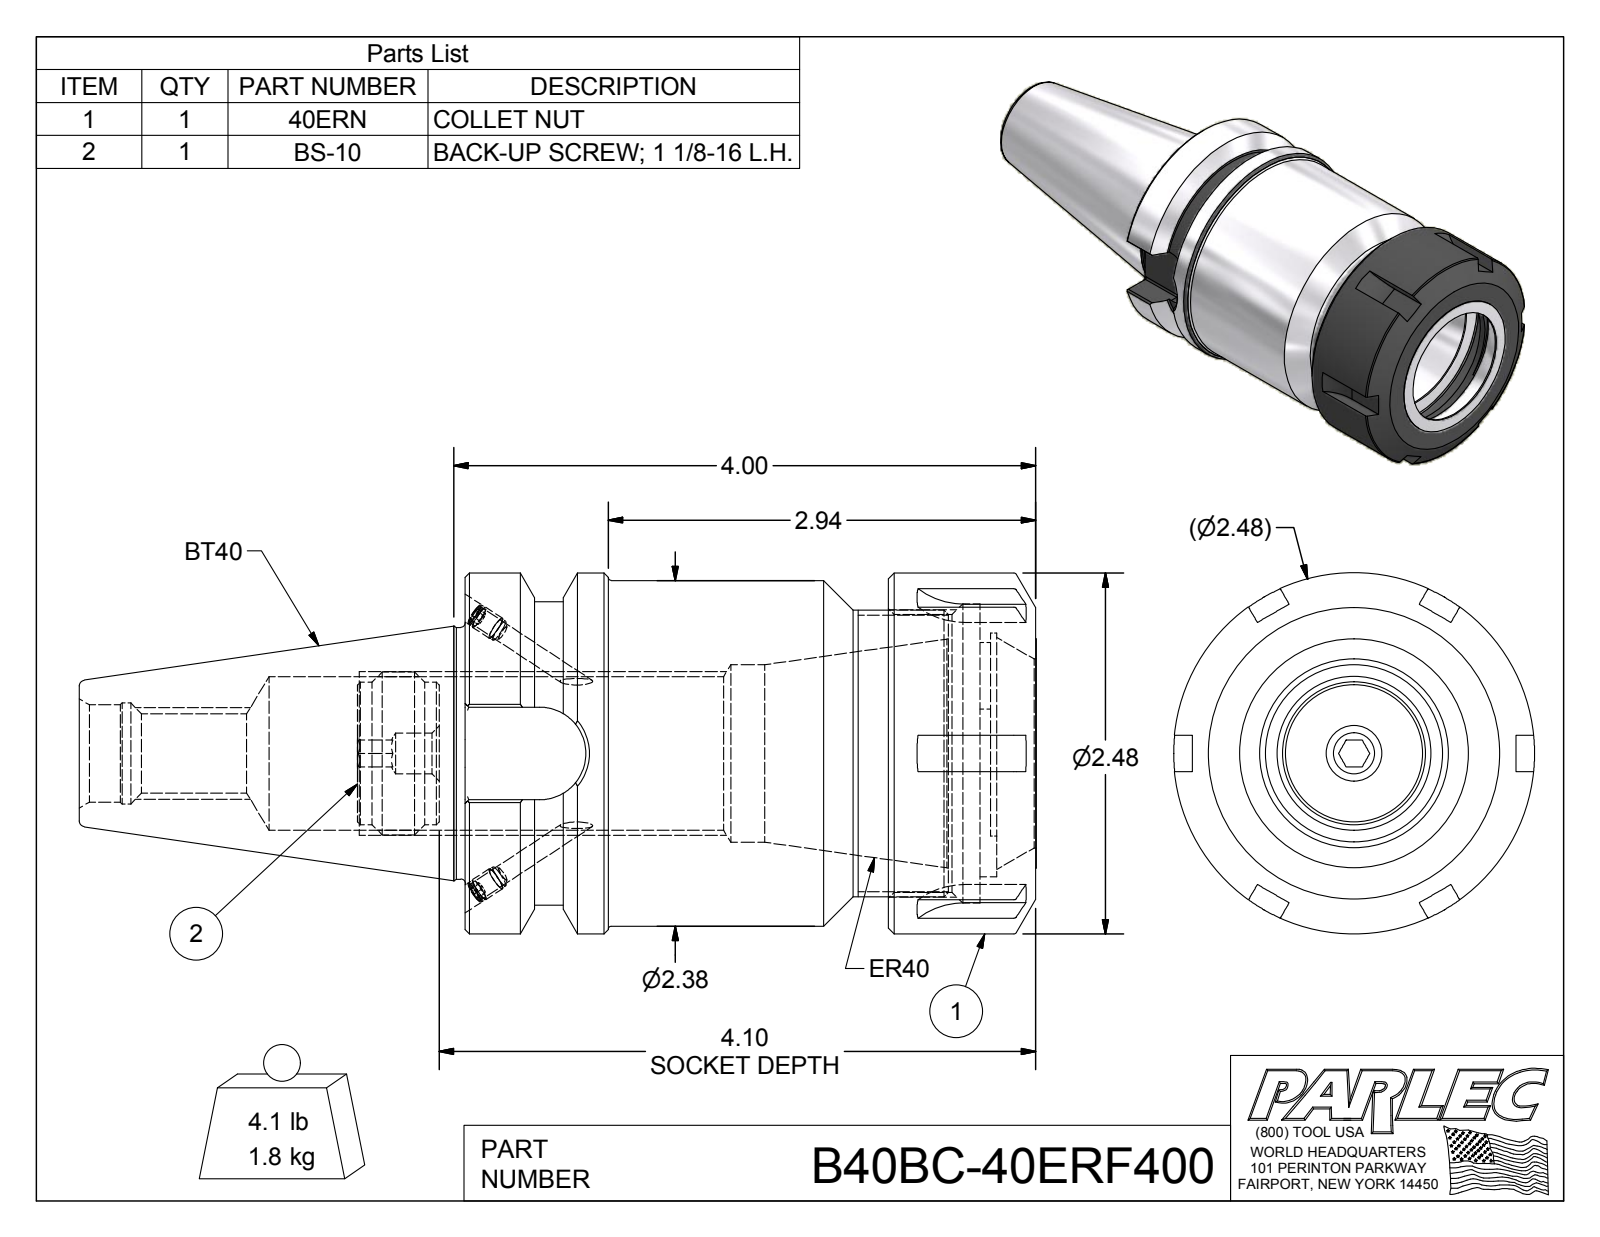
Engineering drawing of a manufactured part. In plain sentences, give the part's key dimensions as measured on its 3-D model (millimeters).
The part is named "B40BCB-40ER4-1; 029-965; 40ERN; BS-10 (+1 more)". Its 3-D file was written by "Autodesk Inventor 2016 (AUTOMOTIVE_DESIGN)". It is 5 solids with 212 faces: 88 planar, 57 cylindrical and 67 other. Overall it measures 167 by 63 by 63 millimeters. Its volume is 241 108 cubic millimeters and its surface area 56 498 square millimeters. Round holes: 2 of diameter 3.3, 2 of diameter 4.1, 1 of diameter 5.59, 1 of diameter 7.11, 1 of diameter 13.84, 1 of diameter 17.01, 1 of diameter 17.62, 1 of diameter 26.85, 1 of diameter 30.99, 1 of diameter 33.02, 1 of diameter 41.1, 1 of diameter 48.5. Round bosses or shafts: 2 of diameter 4.2, 2 of diameter 4, 1 of diameter 63, 1 of diameter 62.99, 1 of diameter 60.32, 1 of diameter 53.01, 1 of diameter 50, 1 of diameter 43.94. Partial cylindrical surfaces (rounded edges, fillets, slot ends): 20 of radius 0.51, 1 of radius 8.09, 1 of radius 18.5, 1 of radius 21. The main face-to-face distances are 99.62, 73.59, 26.03, 89.72, 16.13, 9.9, 84.38, 10.79, 5.34, 15.24. The hole center spacings are 2.29.
